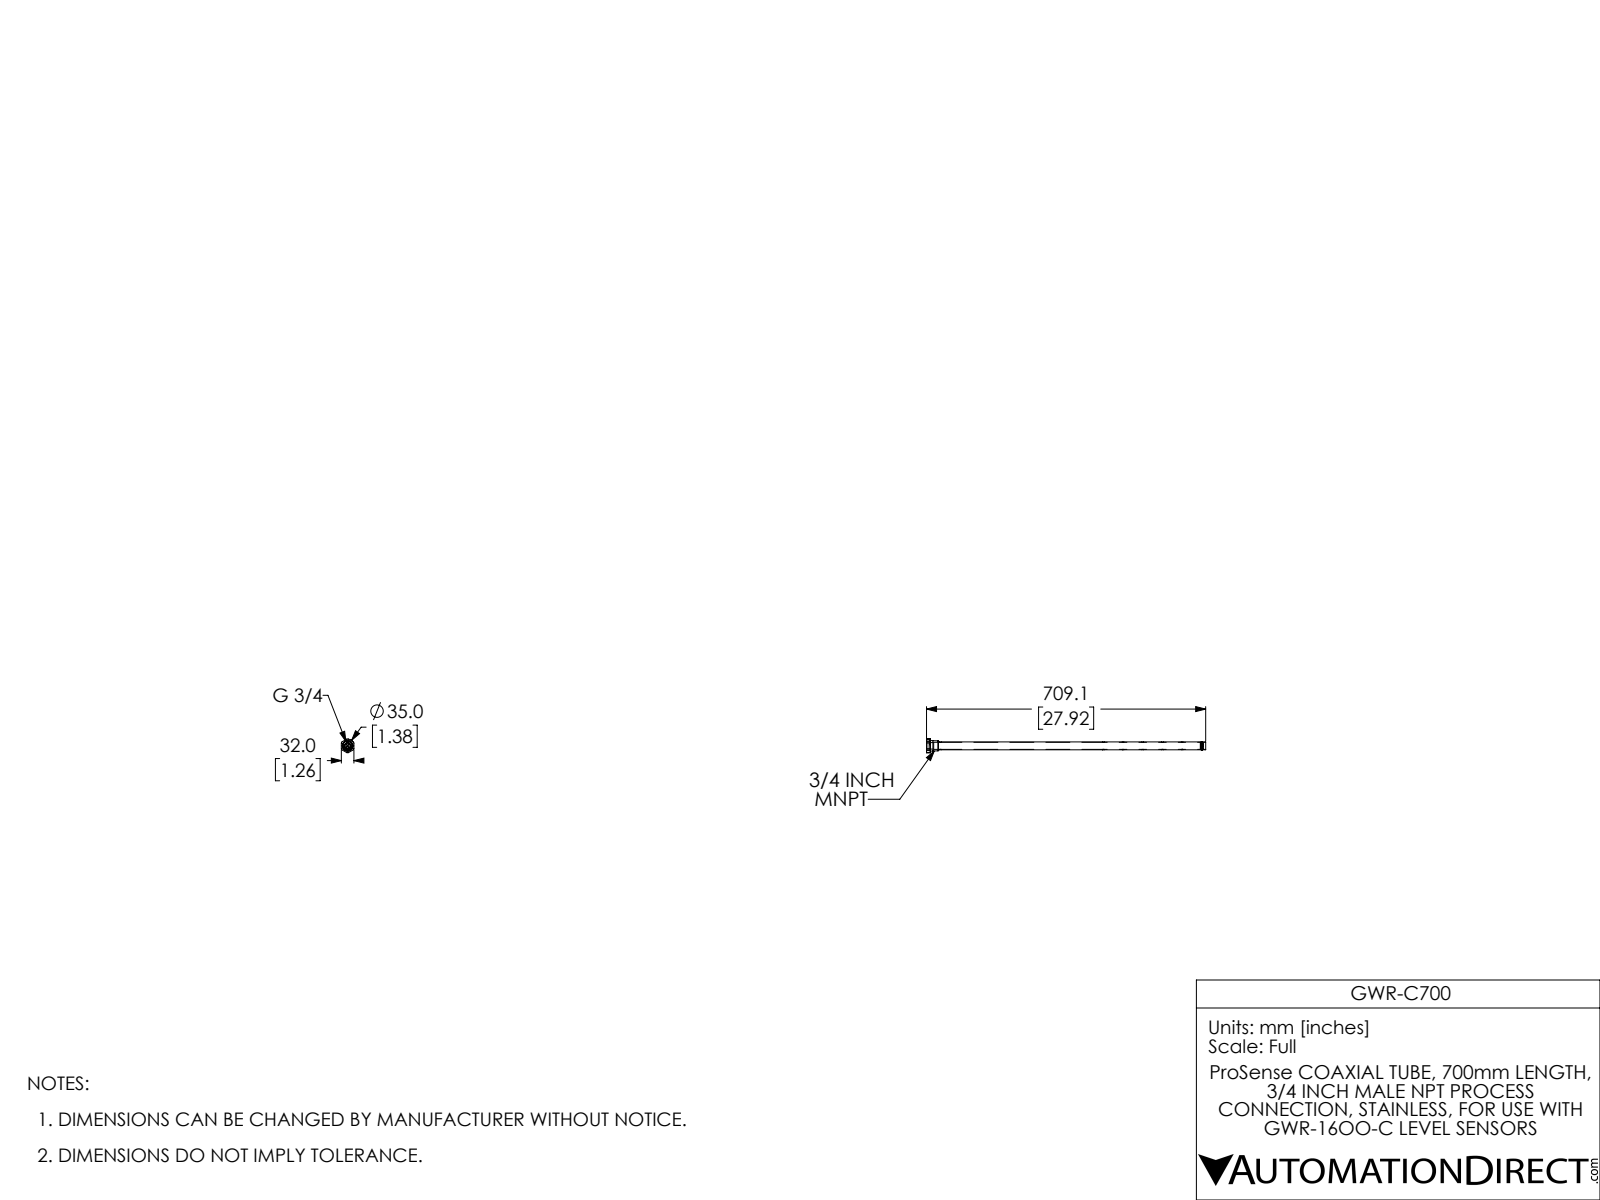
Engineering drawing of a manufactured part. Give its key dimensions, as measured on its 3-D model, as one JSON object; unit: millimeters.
{"part_name": "GWR-C700", "step_written_by": "SolidWorks 2017 (AUTOMOTIVE_DESIGN)", "units": "millimeters", "bodies": {"solids": 1, "faces": 125, "planar": 19, "cylindrical": 84, "other": 22}, "overall_size": [709.1, 35, 32], "volume_mm3": 51090, "surface_area_mm2": 87230, "round_holes": [[4, 7], [16.5, 1], [18, 1], [24.1, 1]], "round_bosses_or_shafts": [[26.7, 1], [20, 1]], "partial_cylinders_radius": [[1.9, 8], [4, 1], [7, 1], [7.5, 1], [17.5, 1]], "face_to_face_distances": [32, 10, 0.9, 9.1, 20, 20.9, 30, 669.7, 689.7, 690.6], "hole_center_spacings": [50, 100, 150, 200, 250, 414, 464, 514]}
